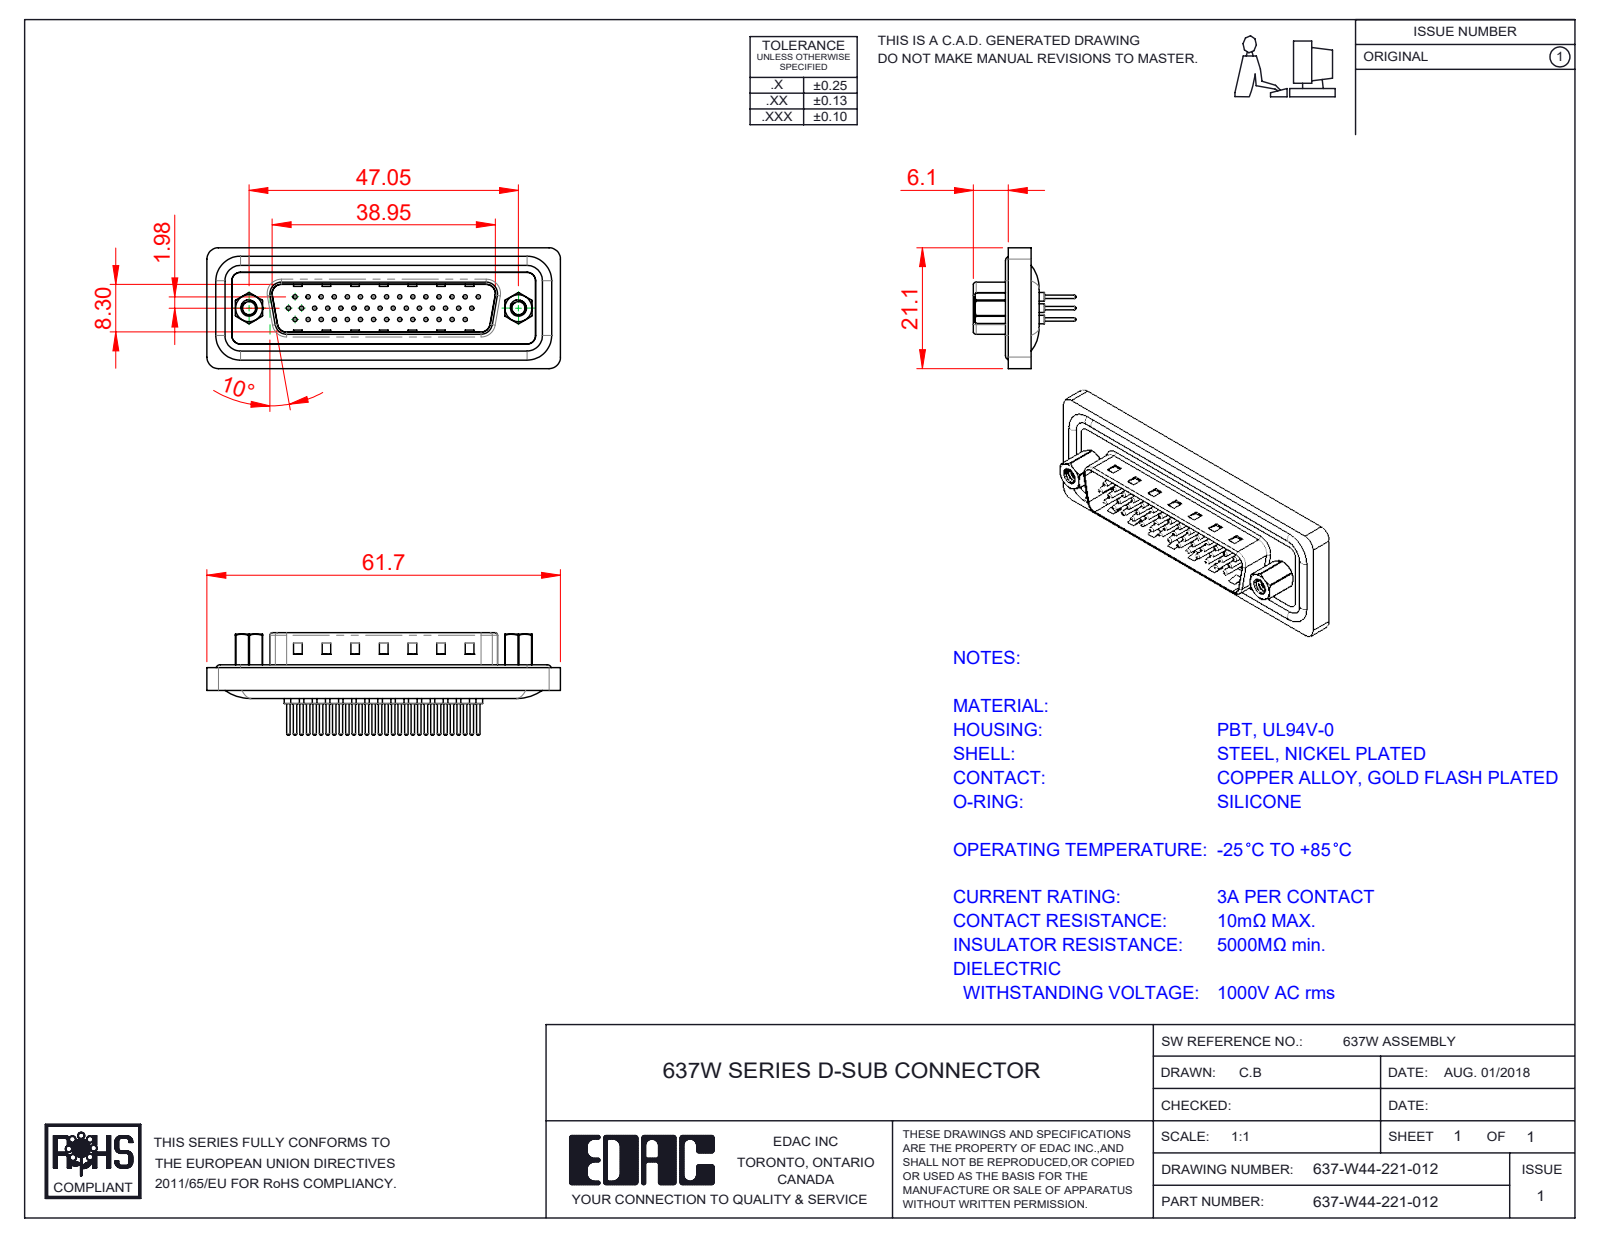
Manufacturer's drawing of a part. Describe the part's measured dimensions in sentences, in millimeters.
The part is named "637W Contact Row 3_21; 637W Contact Row 2_21; 637W Housing_44 Contacts; 637W Shell_44 Contacts (+5 more)". Its 3-D file was written by "SolidWorks 2016 (CONFIG_CONTROL_DESIGN)". It is 52 solids with 2234 faces: 513 planar, 920 cylindrical and 801 other. Overall it measures 61.74 by 21.1 by 17.9 millimeters. Its volume is 6 372 cubic millimeters and its surface area 12 028 square millimeters. Round holes: 44 of diameter 0.75, 44 of diameter 1.5, 44 of diameter 1.6, 44 of diameter 2, 2 of diameter 2.26, 2 of diameter 2.29, 2 of diameter 4, 2 of diameter 4.8, 2 of diameter 5. Round bosses or shafts: 44 of diameter 0.6, 21 of diameter 1.5, 4 of diameter 1.6, 2 of diameter 4.9, 2 of diameter 2.79, 1 of diameter 5. Partial cylindrical surfaces (rounded edges, fillets, slot ends): 14 of radius 2, 13 of radius 1.5, 8 of radius 0.5, 6 of radius 2.7, 4 of radius 0.9, 4 of radius 1.6, 4 of radius 4.3, 2 of radius 0.4. The main face-to-face distances are 0.4, 1.6, 2.5, 2.9, 1.1, 5.65, 15.45, 0.75, 6.4, 14.7. The hole center spacings are 2.28, 3.96, 2.29, 4.57, 8.24, 6.86, 11.43, 14.99.
